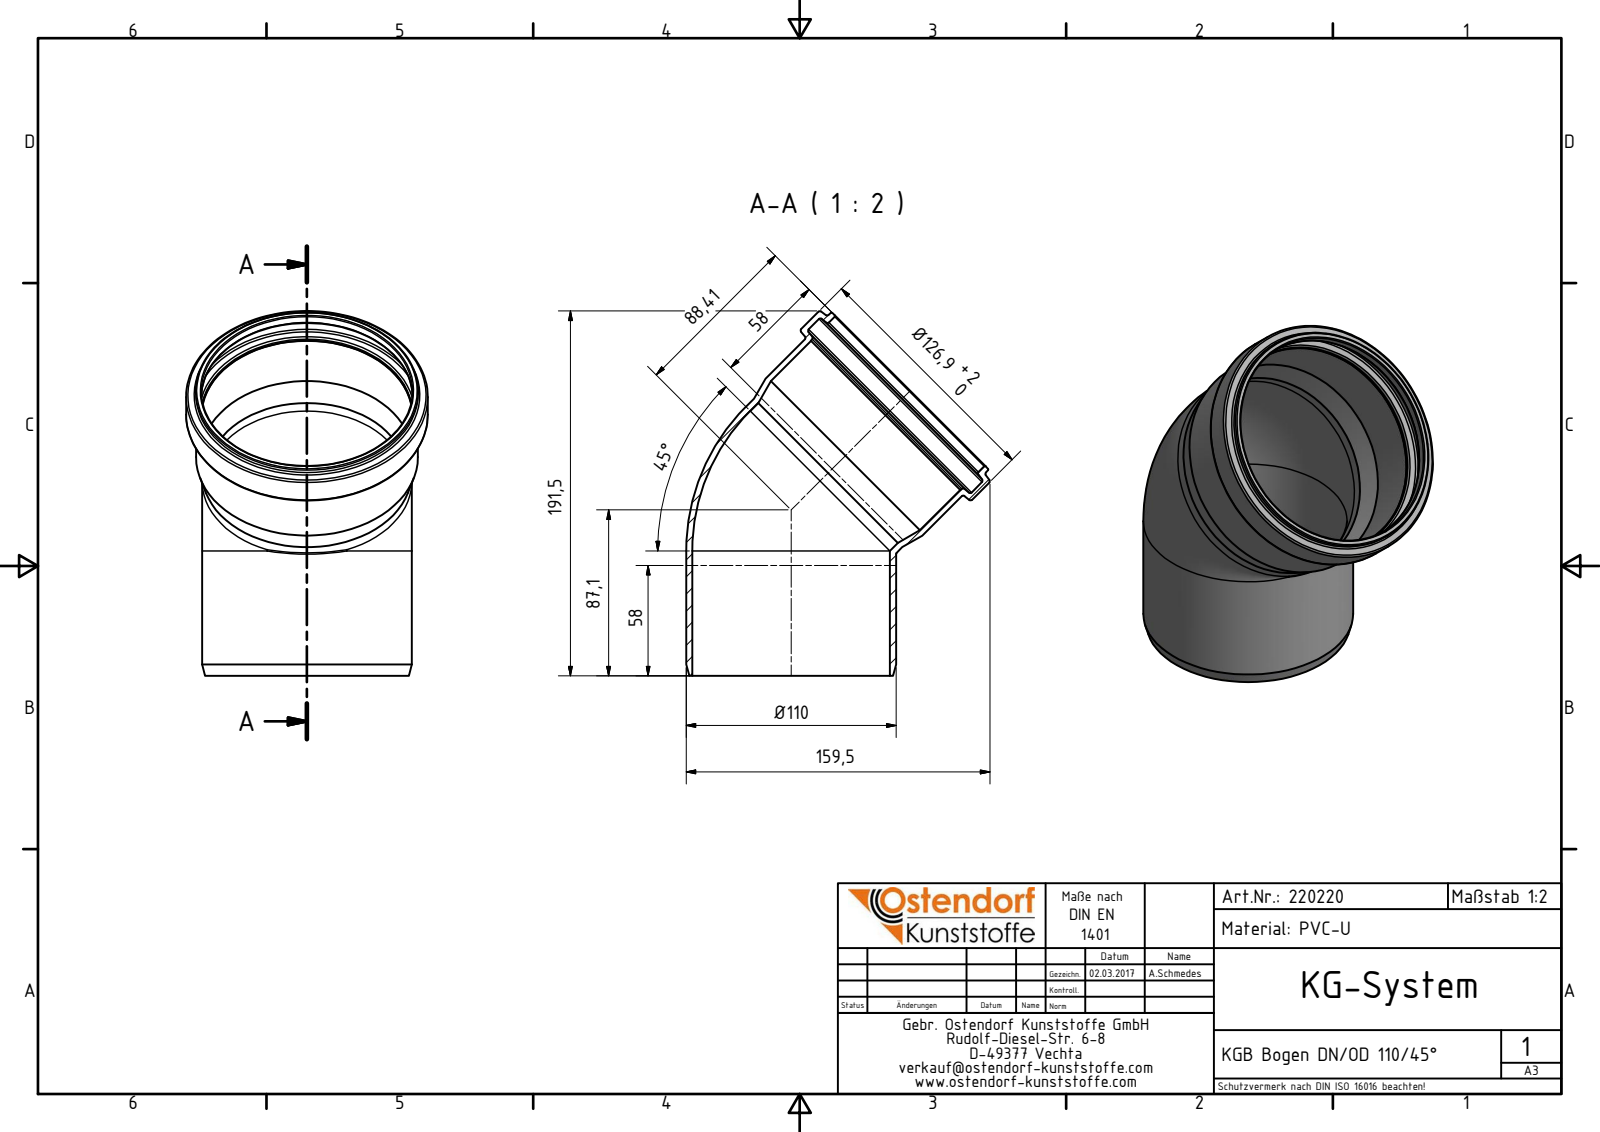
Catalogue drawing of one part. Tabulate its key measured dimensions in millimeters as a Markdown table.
| quantity | value |
| --- | --- |
| part name | 220220 KGB Bogen DN_OD 110_45° |
| STEP written by | Autodesk Inventor 2016 (AUTOMOTIVE_DESIGN) |
| units | millimeters |
| bodies | 1 solid, 34 faces (3 planar, 11 cylindrical, 20 other) |
| overall size | 191.5 × 159.5 × 126.9 |
| volume | 181 944 mm³ |
| surface area | 127 318 mm² |
| round holes (diameter × count) | 103.8 × 2, 110.7 × 1, 111 × 1, 121.1 × 1 |
| round bosses / shafts (diameter × count) | 110.2 × 2, 126.9 × 1, 116.8 × 1, 116.5 × 1 |
| main face-to-face distances | 18.25 |
